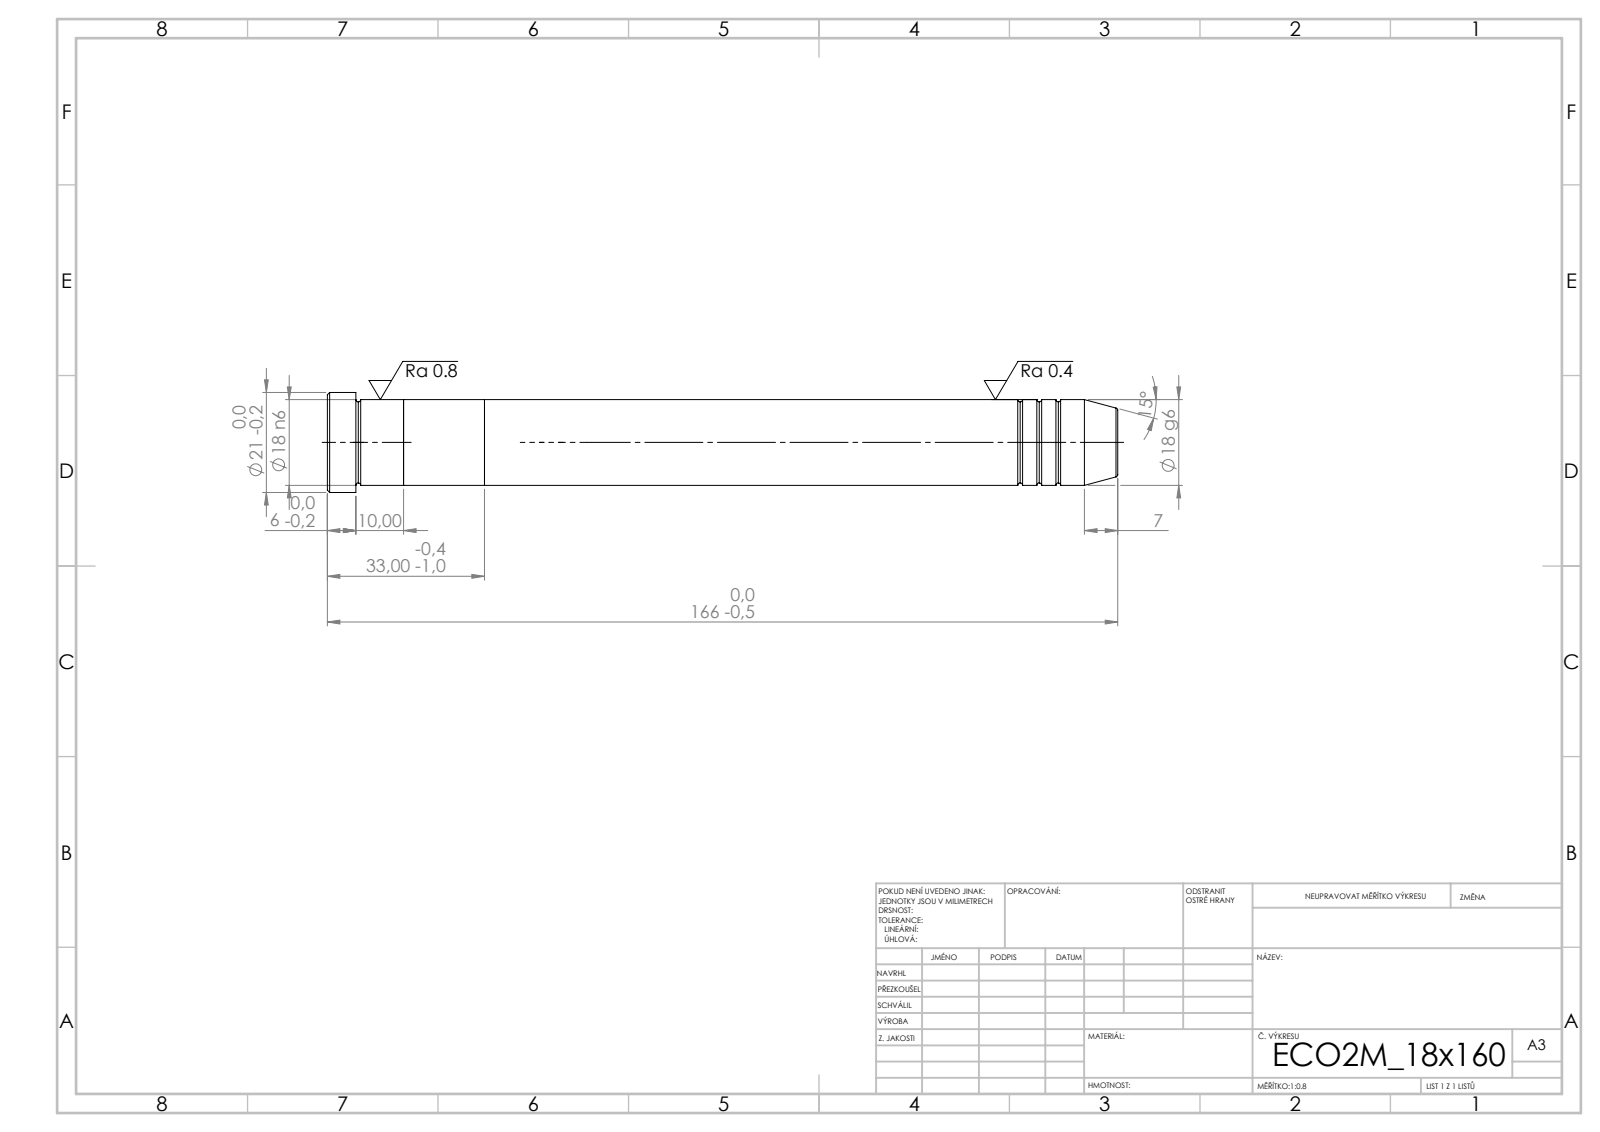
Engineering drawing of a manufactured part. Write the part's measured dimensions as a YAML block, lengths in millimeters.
step_written_by: "SolidWorks 2019 (CONFIG_CONTROL_DESIGN)"
units: millimeters
bodies: {solids: 3, faces: 43, planar: 7, cylindrical: 14, other: 22}
overall_size: [166, 21, 21]
volume: 42352
surface_area: 11122
round_bosses_or_shafts:
  - {diameter: 21, count: 1}
  - {diameter: 18, count: 1}
face_to_face_distances: [17, 33, 16, 133, 150, 166, 160, 27, 10, 6]
